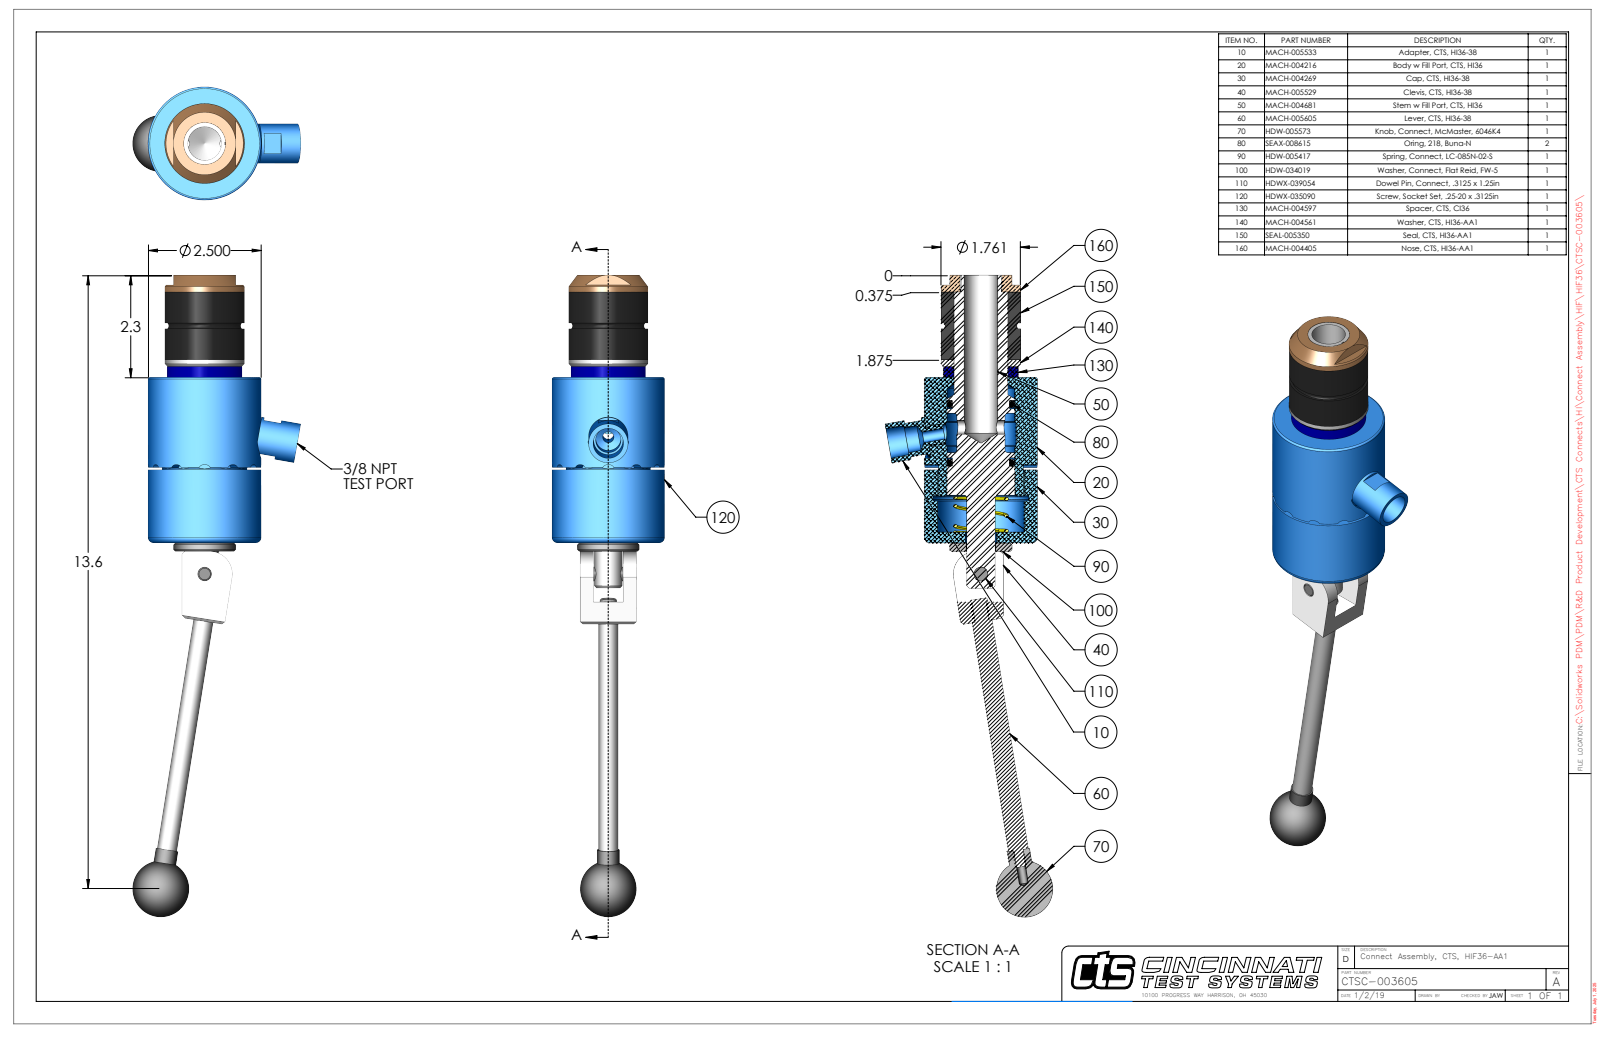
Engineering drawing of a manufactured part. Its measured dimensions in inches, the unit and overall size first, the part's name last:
Units: inches
Overall size (bounding box): 14.215 × 3.716 × 2.5
Round holes (diameter × count): ⌀0.201 ×2, ⌀0.15 ×1, ⌀0.25 ×1, ⌀0.311 ×1, ⌀0.312 ×1, ⌀0.313 ×1, ⌀0.314 ×1, ⌀0.562 ×1, ⌀0.656 ×1, ⌀0.696 ×1, ⌀0.75 ×1, ⌀0.922 ×1
Round bosses / shafts (diameter × count): ⌀2.5 ×1, ⌀1.875 ×1, ⌀1.761 ×1, ⌀1.656 ×1, ⌀1.38 ×1, ⌀1.186 ×1, ⌀1 ×1, ⌀0.904 ×1
Partial cylindrical surfaces — rounded edges, fillets, slot ends (radius × count): R0.12 ×12, R0.029 ×2, R0.19 ×1, R0.195 ×1, R0.448 ×1, R0.47 ×1, R0.5 ×1, R1.174 ×1
Main face-to-face distances: 3.668, 5.555, 1.887, 1.5, 4.055, 0.387, 3.905, 0.237, 0.15, 1.65
Hole centre spacings: 0.74, 2.118, 2.858
Volume: 25.32 in³ · Surface area: 128.3 in²
Bodies: 10 solids, 309 faces (111 planar, 127 cylindrical, 71 other)
Part name (STEP PRODUCT): CTSC-003605
STEP written by: SolidWorks 2023 (AUTOMOTIVE_DESIGN)
